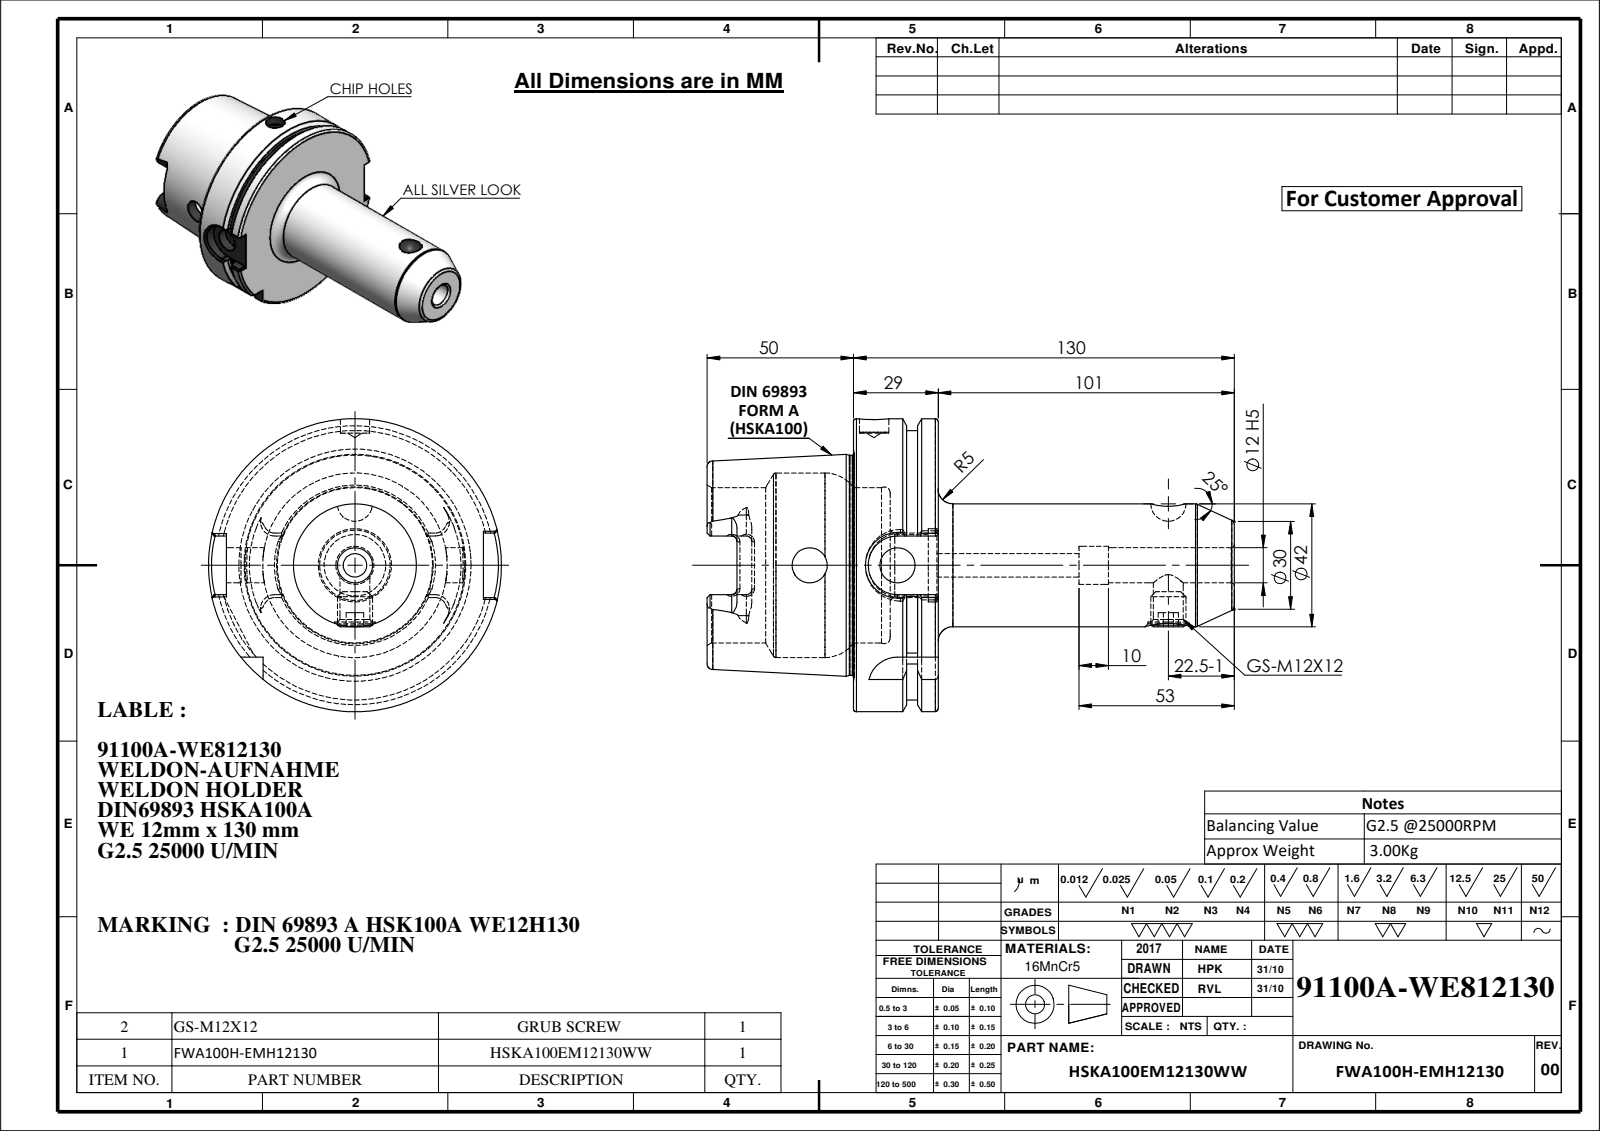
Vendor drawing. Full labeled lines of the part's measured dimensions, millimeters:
Part name (STEP PRODUCT): HSKA100EM12130WW; GS-M12X12-DIN1835-B_ISO 4026 - M12 x 12-N; FWA100H-EMH12130
STEP written by: SolidWorks 2024 (CONFIG_CONTROL_DESIGN)
Units: millimetres
Bodies: 2 solids, 203 faces (63 planar, 58 cylindrical, 82 other)
Overall size (bounding box): 180 × 100 × 100
Volume: 380 494 mm³ · Surface area: 66 463 mm²
Round holes (diameter × count): ⌀12 ×3, ⌀8 ×1, ⌀10 ×1, ⌀10.2 ×1, ⌀13 ×1, ⌀14 ×1, ⌀21 ×1, ⌀25 ×1, ⌀53 ×1, ⌀63 ×1
Round bosses / shafts (diameter × count): ⌀100 ×1, ⌀92 ×1, ⌀75.16 ×1, ⌀42 ×1, ⌀12 ×1
Partial cylindrical surfaces — rounded edges, fillets, slot ends (radius × count): R1.8 ×6, R4.88 ×4, R10 ×2, R11 ×1
Main face-to-face distances: 28.95, 12.5, 16.45, 50, 62.5, 78.95, 180, 130, 117.5, 101.05
Hole centre spacings: 30, 100.5
